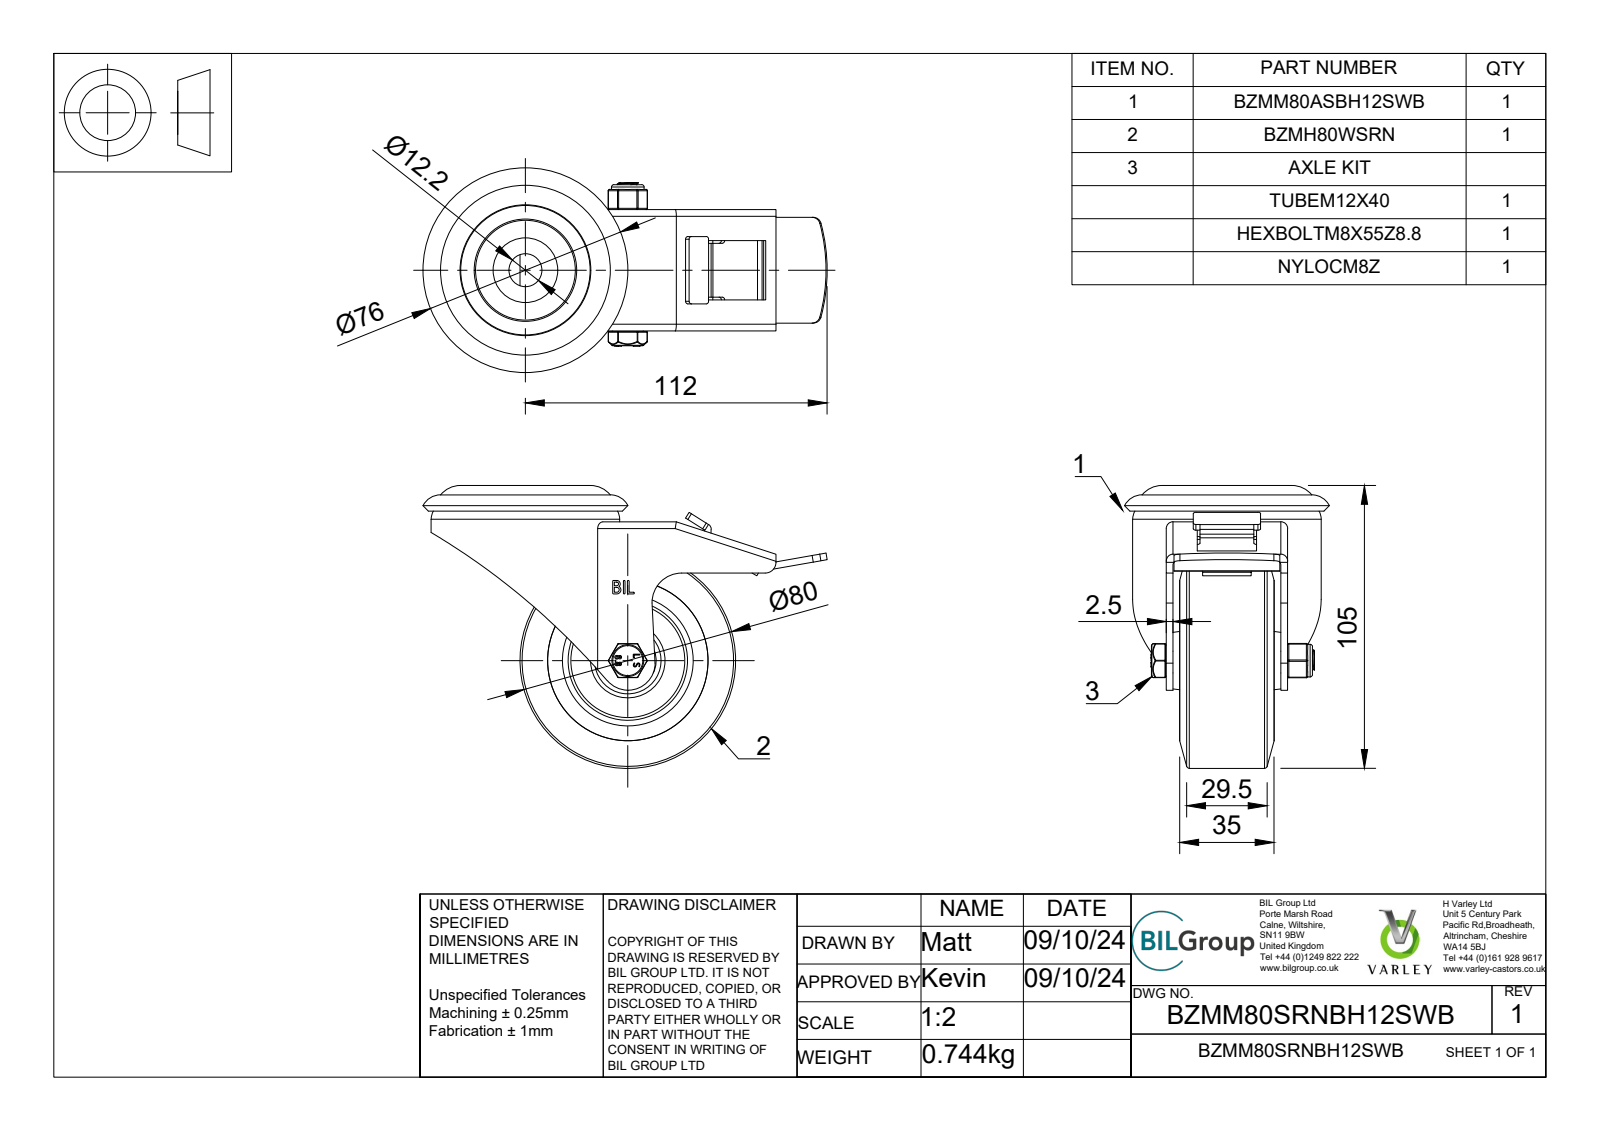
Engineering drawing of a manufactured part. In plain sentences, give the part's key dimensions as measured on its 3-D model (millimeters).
The part is named "BZMM80SRNBH12SWB v3; BZMM80ASBH12SWB v1; ZINC PLATED, PRESSED STEEL HEAD; ZINC PLATED, PRESSED STEEL FORKS (+8 more)". Its 3-D file was written by "Autodesk Translation Framework v13.20.0.188 (AUTOMOTIVE_DESIGN)". It is 10 solids with 591 faces: 275 planar, 211 cylindrical and 105 other. Overall it measures 150 by 105 by 76 millimeters. Its volume is 204 942 cubic millimeters and its surface area 98 832 square millimeters. Round holes: 2 of diameter 0.66, 2 of diameter 12.2, 1 of diameter 8, 1 of diameter 8.2, 1 of diameter 8.4, 1 of diameter 8.6, 1 of diameter 59.5, 1 of diameter 65, 1 of diameter 72. Round bosses or shafts: 1 of diameter 80, 1 of diameter 70, 1 of diameter 49.5, 1 of diameter 38, 1 of diameter 24, 1 of diameter 21.31, 1 of diameter 12.1, 1 of diameter 11.9. Partial cylindrical surfaces (rounded edges, fillets, slot ends): 48 of radius 0.75, 26 of radius 0.5, 12 of radius 0.25, 6 of radius 1, 6 of radius 1.25, 5 of radius 2, 5 of radius 2.5, 4 of radius 0.33. The main face-to-face distances are 2.5, 40, 42.5, 8, 5, 37.5, 4.5, 45, 24, 21.5. The hole center spacings are 3.22, 2.49.
